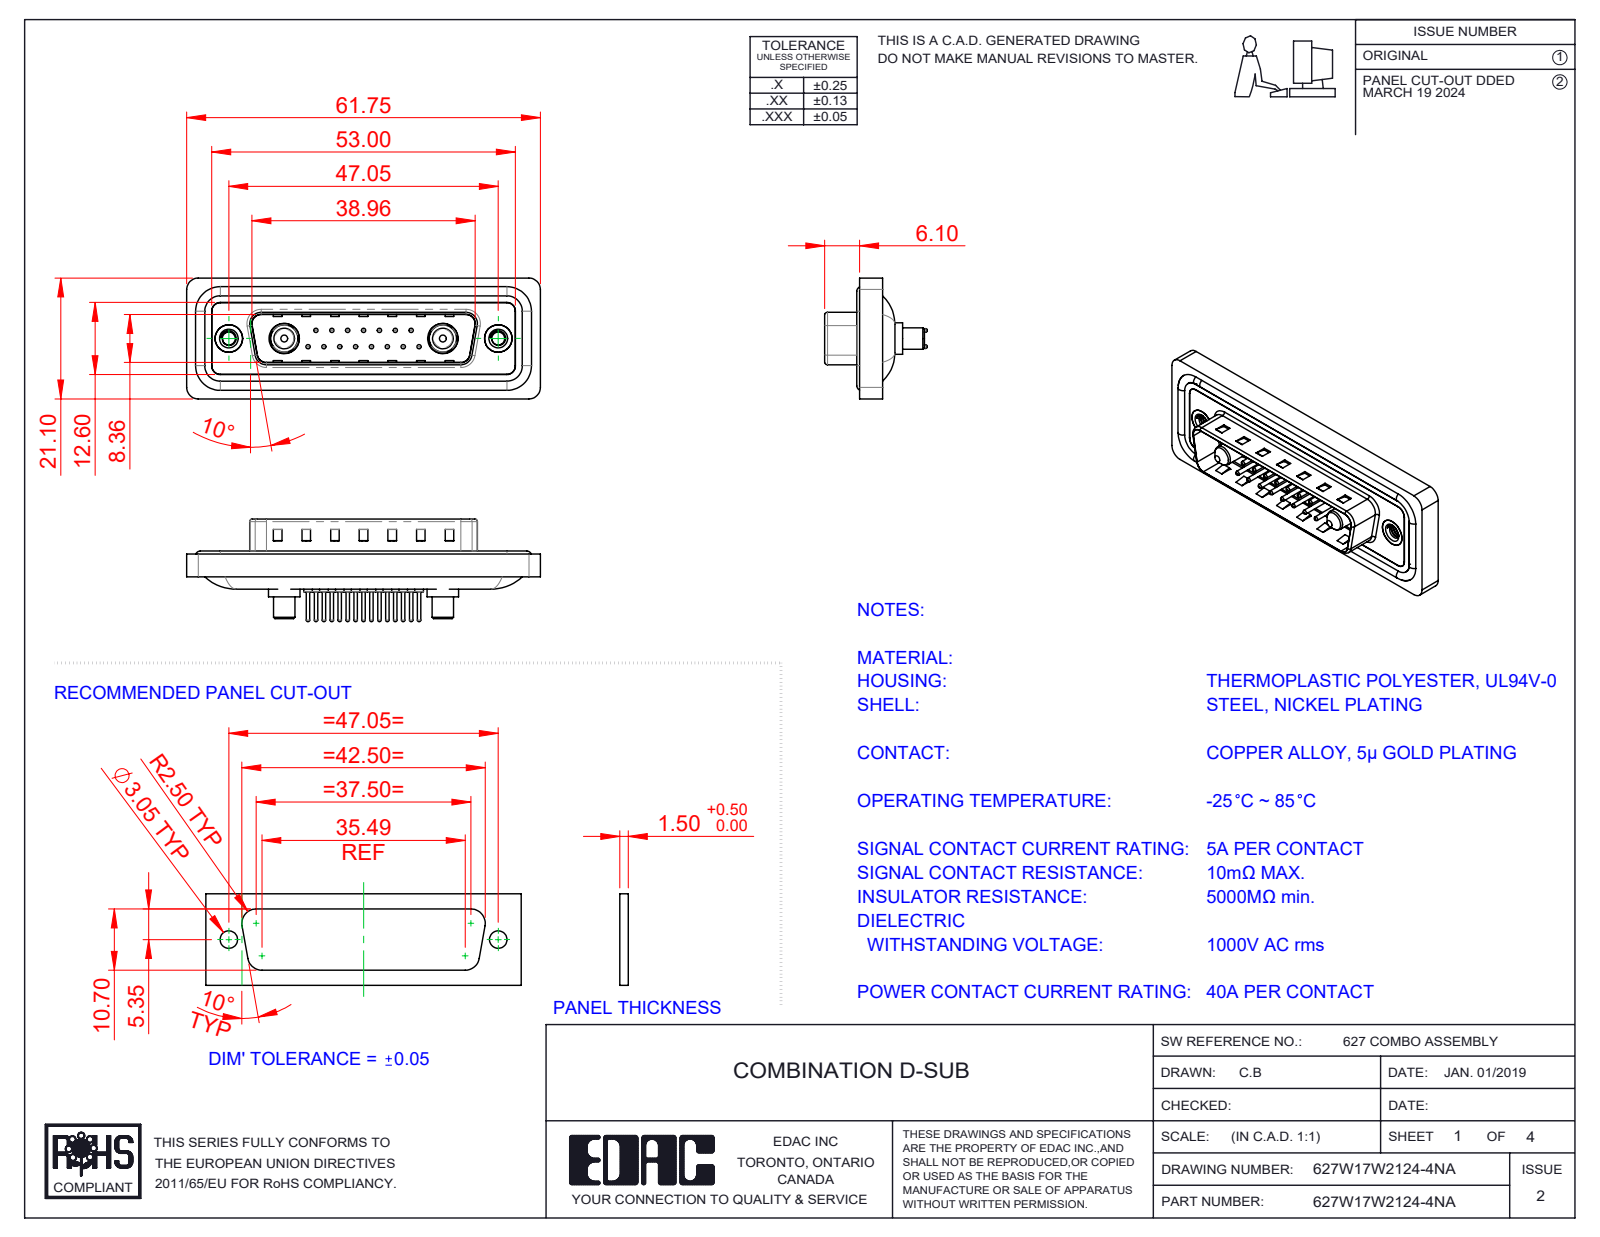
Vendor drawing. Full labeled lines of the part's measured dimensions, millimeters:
Part name (STEP PRODUCT): 627Combo Threaded Rivet_A; Power Pin_40A S; 627Combo Shell Front_25 Contacts; 627W17W2124-4NA (+5 more)
STEP written by: SolidWorks 2023 (CONFIG_CONTROL_DESIGN)
Units: millimetres
Bodies: 26 solids, 1114 faces (334 planar, 438 cylindrical, 342 other)
Overall size (bounding box): 61.75 × 21.1 × 17.9
Volume: 7 305 mm³ · Surface area: 11 933 mm²
Round holes (diameter × count): ⌀0.75 ×15, ⌀1.6 ×15, ⌀2 ×15, ⌀2.26 ×2, ⌀4 ×2, ⌀4.8 ×2, ⌀4.85 ×2, ⌀5 ×2, ⌀5.3 ×2
Round bosses / shafts (diameter × count): ⌀1.5 ×15, ⌀0.6 ×15, ⌀1.6 ×4, ⌀5.5 ×2, ⌀5.2 ×2, ⌀4.9 ×2, ⌀4.75 ×2, ⌀3.75 ×2
Partial cylindrical surfaces — rounded edges, fillets, slot ends (radius × count): R1.5 ×22, R2 ×18, R0.5 ×8, R1.6 ×8, R0.25 ×4, R0.6 ×4, R0.65 ×4, R0.9 ×4
Main face-to-face distances: 0.4, 1.5, 1.1, 1.6, 0.5, 3.1, 2.9, 0.82, 9.58, 4.1
Hole centre spacings: 3.16, 2.77, 5.54, 8.31, 5.04, 7.49, 11.08, 5.03
